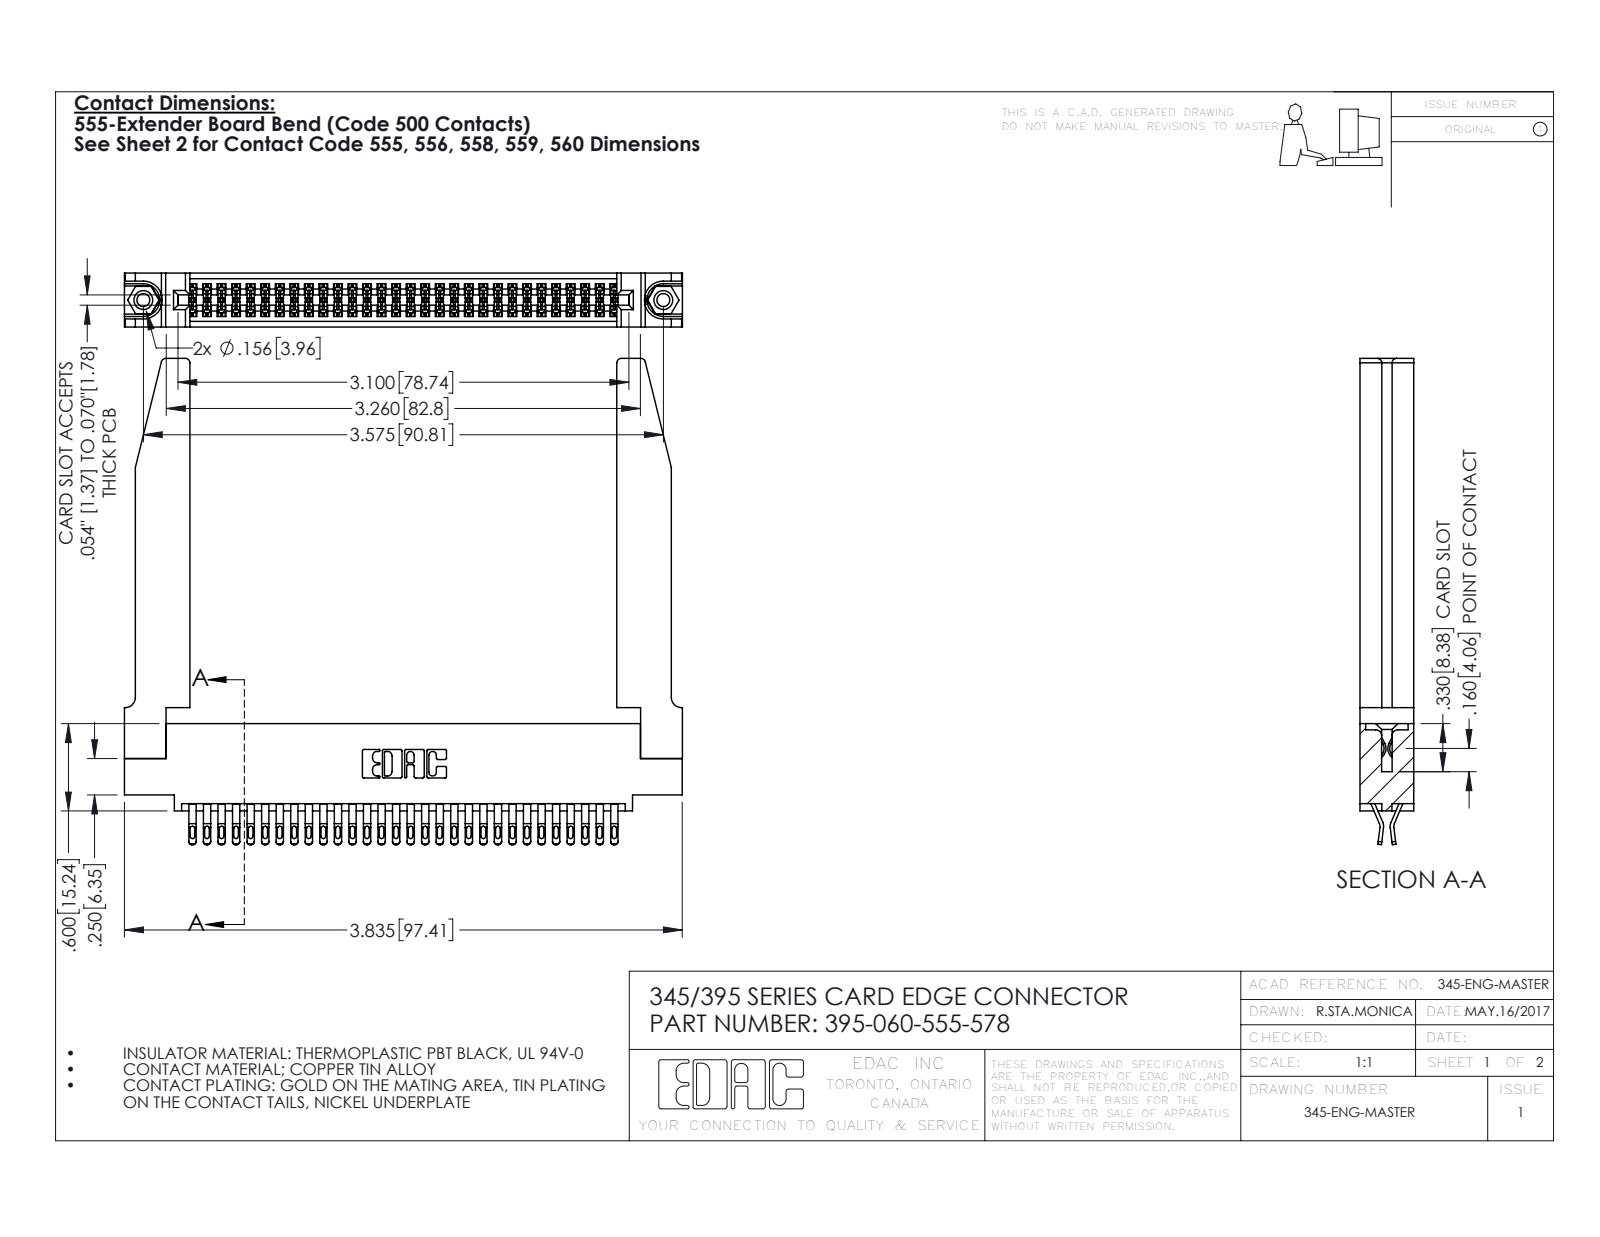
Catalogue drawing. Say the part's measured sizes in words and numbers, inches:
The part is named "345 Part_0.110 Offset - 0.156 Dia-TH; 345-250-001_345-250-001-102; 395-060-555-578; 345-220-078_345-220-078 (+1 more)". Its 3-D file was written by "SolidWorks 2016 (CONFIG_CONTROL_DESIGN)". It is 65 solids with 3724 faces: 2086 planar, 1586 cylindrical and 52 other. Overall it measures 3.836 by 3.342 by 0.37 inches. Its volume is 1.051 cubic inches and its surface area 32.98 square inches. Round holes: 2 of diameter 0.089, 2 of diameter 0.125, 2 of diameter 0.156, 1 of diameter 0.064. Round bosses or shafts: 2 of diameter 0.155. Partial cylindrical surfaces (rounded edges, fillets, slot ends): 150 of radius 0.016, 120 of radius 0.02, 90 of radius 0.006, 22 of radius 0.01, 8 of radius 0.03, 6 of radius 0.007, 6 of radius 0.031, 3 of radius 0.026. The main face-to-face distances are 0.37, 0.072, 0.298, 0.025, 0.2, 0.098, 0.272, 0.225, 0.148, 0.15. The hole center spacings are 0.27, 3.34, 3.575.
